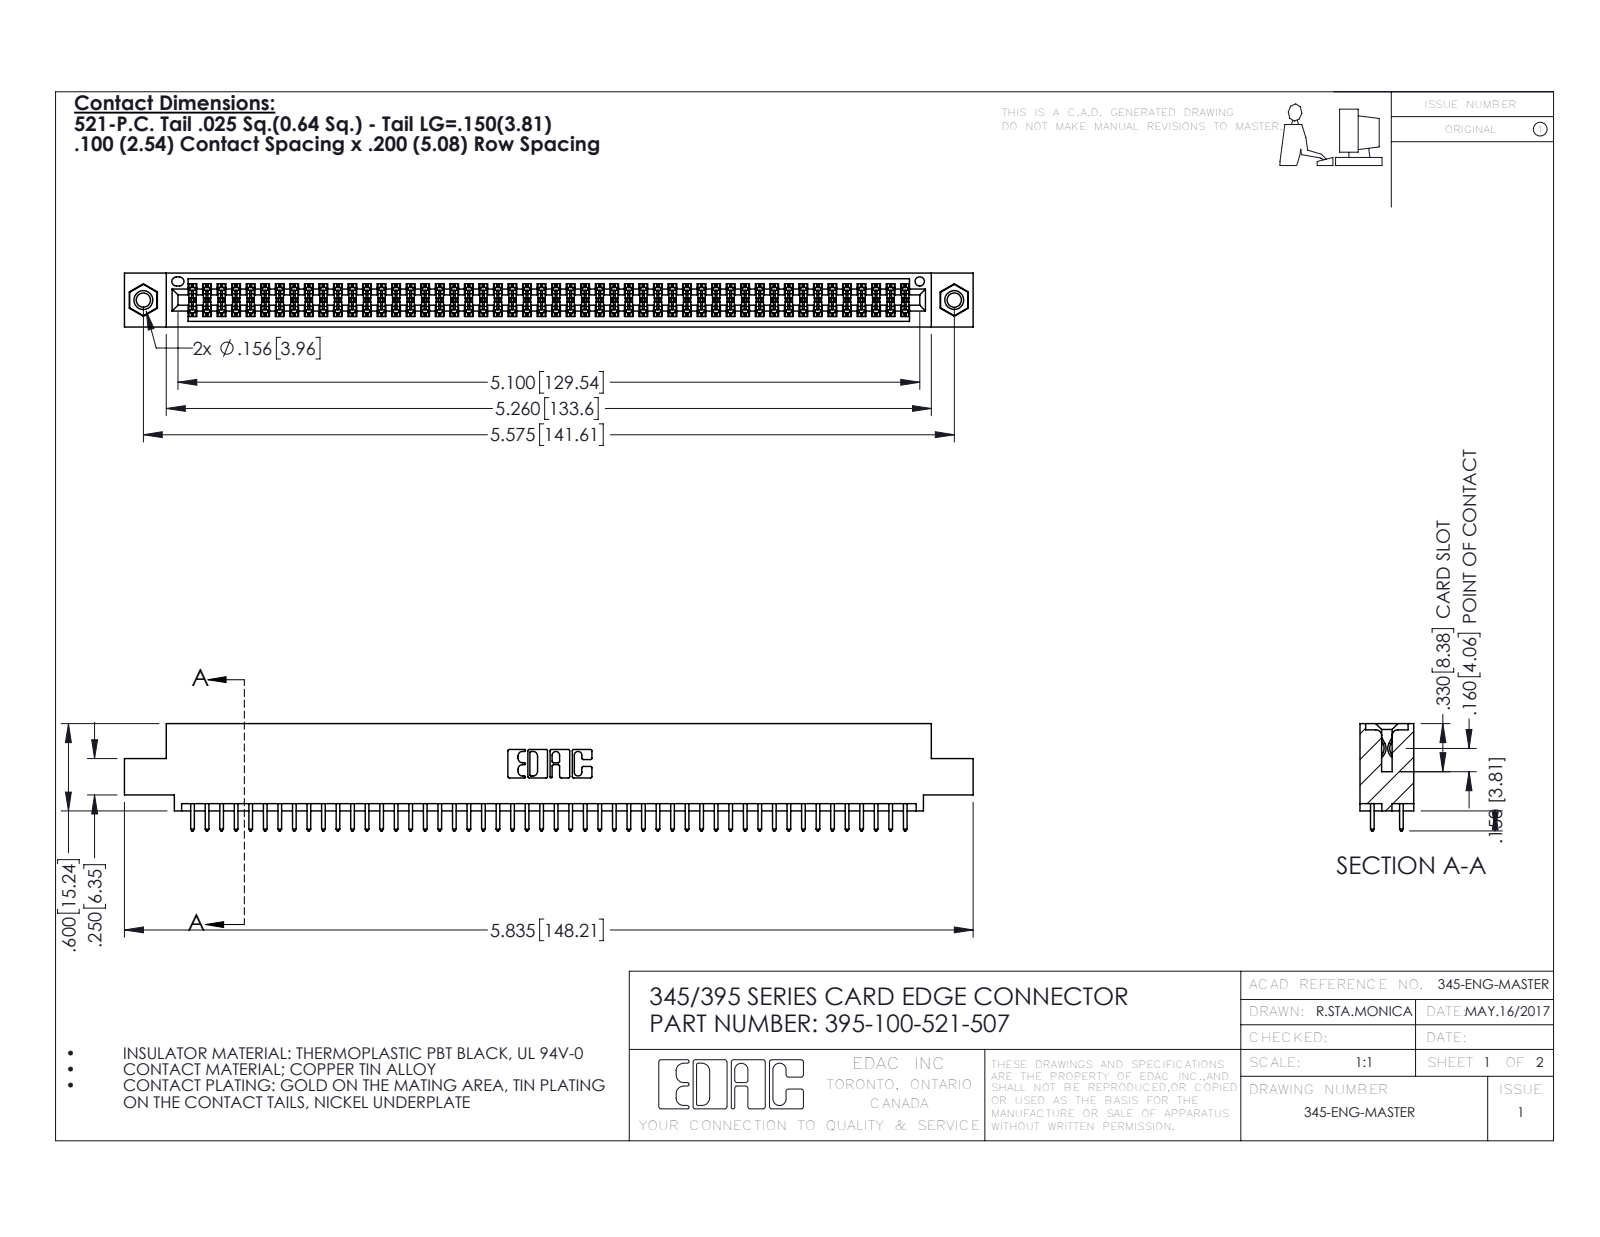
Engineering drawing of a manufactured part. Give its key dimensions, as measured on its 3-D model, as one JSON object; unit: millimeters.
{"part_name": "345 Part_0.110 Offset - 0.156 Dia-TI; 395-100-521-507; 345-292-001_345-293-121; 345-250-001_345-250-005-103", "step_written_by": "SolidWorks 2016 (CONFIG_CONTROL_DESIGN)", "units": "millimeters", "bodies": {"solids": 103, "faces": 5190, "planar": 3416, "cylindrical": 1758, "other": 16}, "overall_size": [148.2, 18.7, 9.4], "volume_mm3": 14300, "surface_area_mm2": 21210, "round_holes": [[2.5, 2], [3.2, 2], [4, 2], [1.6, 1]], "round_bosses_or_shafts": [[3.9, 2]], "partial_cylinders_radius": [[0.2, 150], [0.3, 100], [0.3, 22], [0.2, 6], [0.8, 6], [0.7, 3], [0.4, 2], [0.5, 2]], "face_to_face_distances": [1.8, 7.6, 5.1, 9.4, 2.5, 6.9, 0.6, 5.7, 4.4, 3.8], "hole_center_spacings": [6.9, 135.6, 141.6]}
